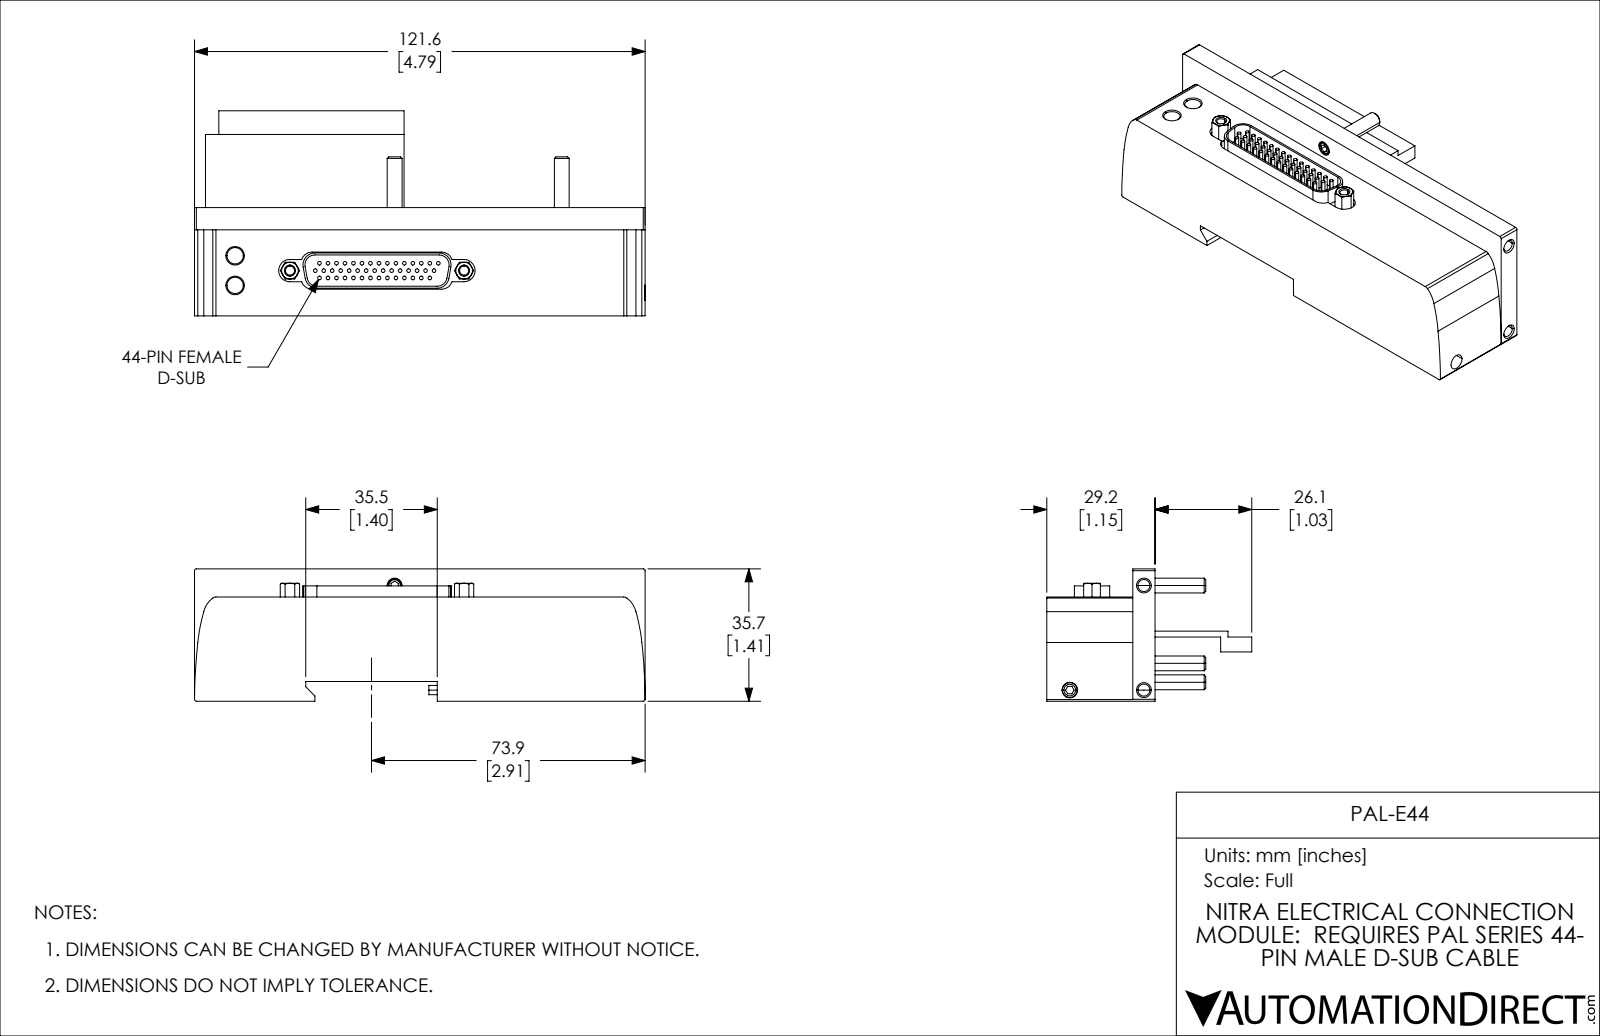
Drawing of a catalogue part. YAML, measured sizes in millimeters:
part_name: "PAL-E44"
step_written_by: "SolidWorks 2019 (CONFIG_CONTROL_DESIGN)"
units: millimeters
bodies: {solids: 1, faces: 451, planar: 143, cylindrical: 248, other: 60}
overall_size: [121.6, 55.3, 35.7]
volume: 58623
surface_area: 36557
round_holes:
  - {diameter: 0.5, count: 50}
  - {diameter: 3.24, count: 2}
  - {diameter: 2.46, count: 1}
  - {diameter: 2.46, count: 1}
  - {diameter: 4.2, count: 1}
round_bosses_or_shafts:
  - {diameter: 0.98, count: 44}
  - {diameter: 4, count: 4}
  - {diameter: 2.5, count: 1}
partial_cylinders:
  - {radius: 3, count: 9}
  - {radius: 5, count: 5}
  - {radius: 0.5, count: 4}
  - {radius: 1.5, count: 4}
  - {radius: 2.68, count: 4}
  - {radius: 3.21, count: 4}
  - {radius: 6.5, count: 4}
  - {radius: 1.4, count: 2}
face_to_face_distances: [1.6, 8, 17.3, 18.9, 29.2, 6.4, 8.6, 25.3, 20, 8.7]
hole_center_spacings: [2, 2.83, 4, 4.47, 6, 6.32, 8, 8.25]
